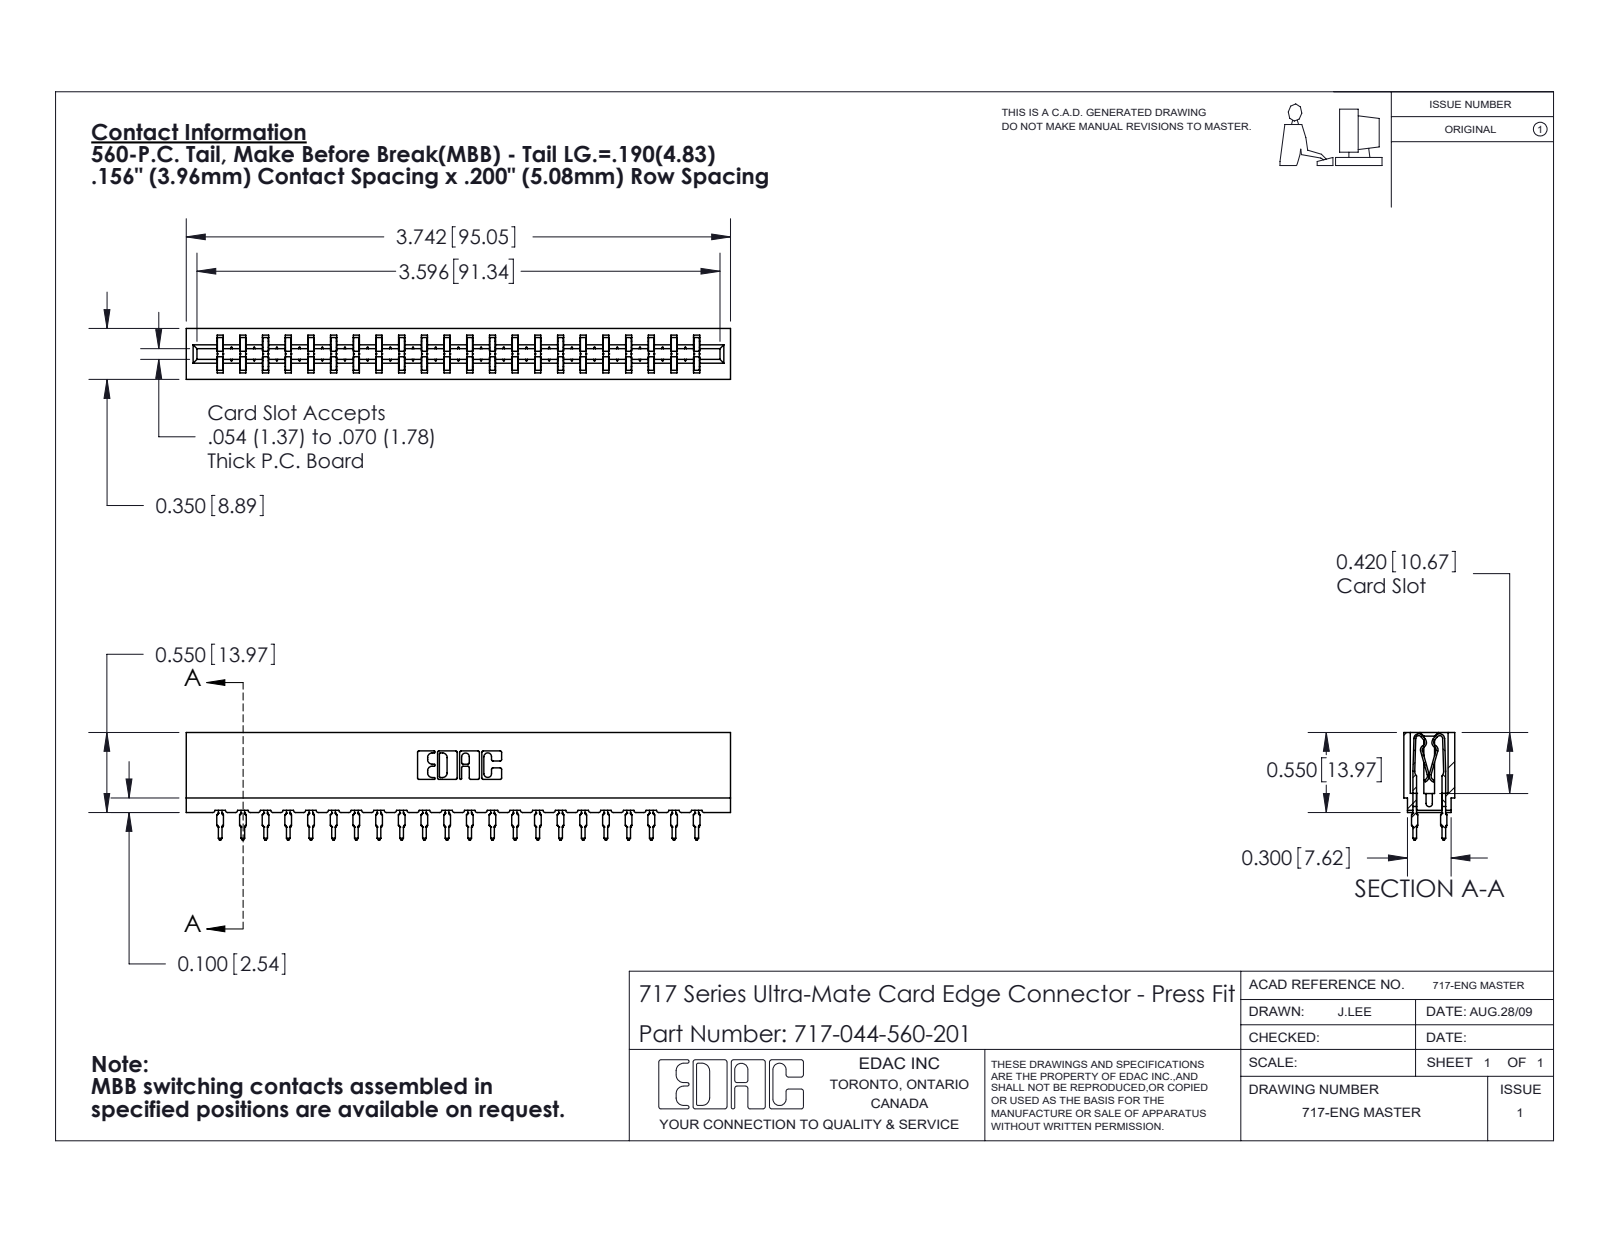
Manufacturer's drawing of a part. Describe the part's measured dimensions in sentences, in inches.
The part is named "717-044-560-201; 717 Part_Insulator Option - 06; 745-292-001_560". Its 3-D file was written by "SolidWorks 2020 (CONFIG_CONTROL_DESIGN)". It is 45 solids with 4450 faces: 2320 planar, 986 cylindrical and 1144 other. Overall it measures 3.742 by 0.739 by 0.35 inches. Its volume is 0.518 cubic inches and its surface area 20.89 square inches. Partial cylindrical surfaces (rounded edges, fillets, slot ends): 88 of radius 0.021, 44 of radius 0.015, 22 of radius 0.01, 8 of radius 0.005, 8 of radius 0.011, 6 of radius 0.007, 6 of radius 0.031, 3 of radius 0.026. The main face-to-face distances are 0.212, 0.138, 0.35, 0.156, 0.063, 0.287, 0.076, 0.149, 0.074, 0.624.
